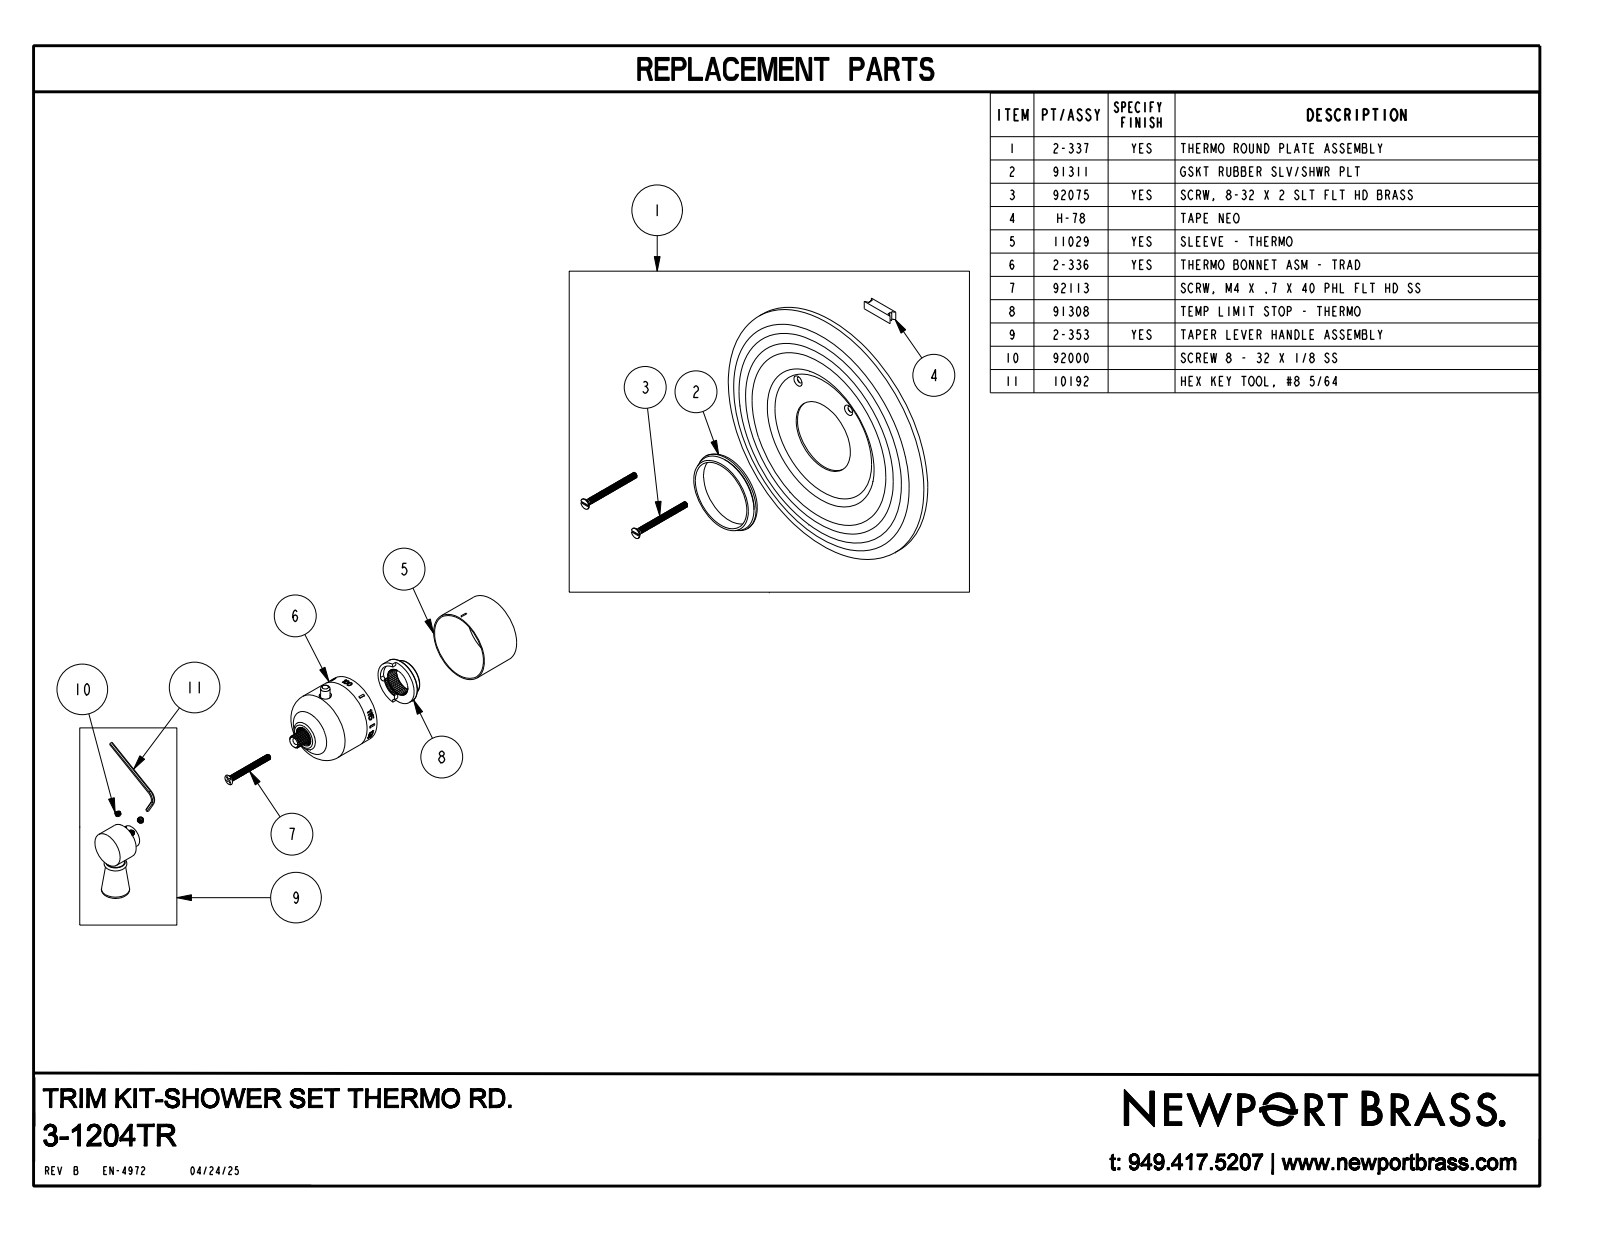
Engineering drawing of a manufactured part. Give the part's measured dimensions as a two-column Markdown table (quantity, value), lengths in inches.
| quantity | value |
| --- | --- |
| part name | 3-1204TR |
| STEP written by | CREO PARAMETRIC BY PTC INC, 2018400 (CONFIG_CONTROL_DESIGN) |
| units | inches |
| bodies | 1 solid, 411 faces (332 planar, 41 cylindrical, 38 other) |
| overall size | 7.5 × 7.5 × 3.739 |
| volume | 25.17 in³ |
| surface area | 116.7 in² |
| round holes (diameter × count) | 0.385 × 1 |
| round bosses / shafts (diameter × count) | 7.5 × 1, 1.97 × 1, 1.94 × 1, 1.929 × 1, 0.98 × 1, 0.625 × 1, 0.37 × 1, 0.365 × 1 |
| partial cylindrical surfaces (radius × count) | 0.969 × 1 |
| main face-to-face distances | 0.313, 0.159, 0.471, 3.031, 2.719, 2.56, 2.706, 2.393, 2.234, 0.326 |
